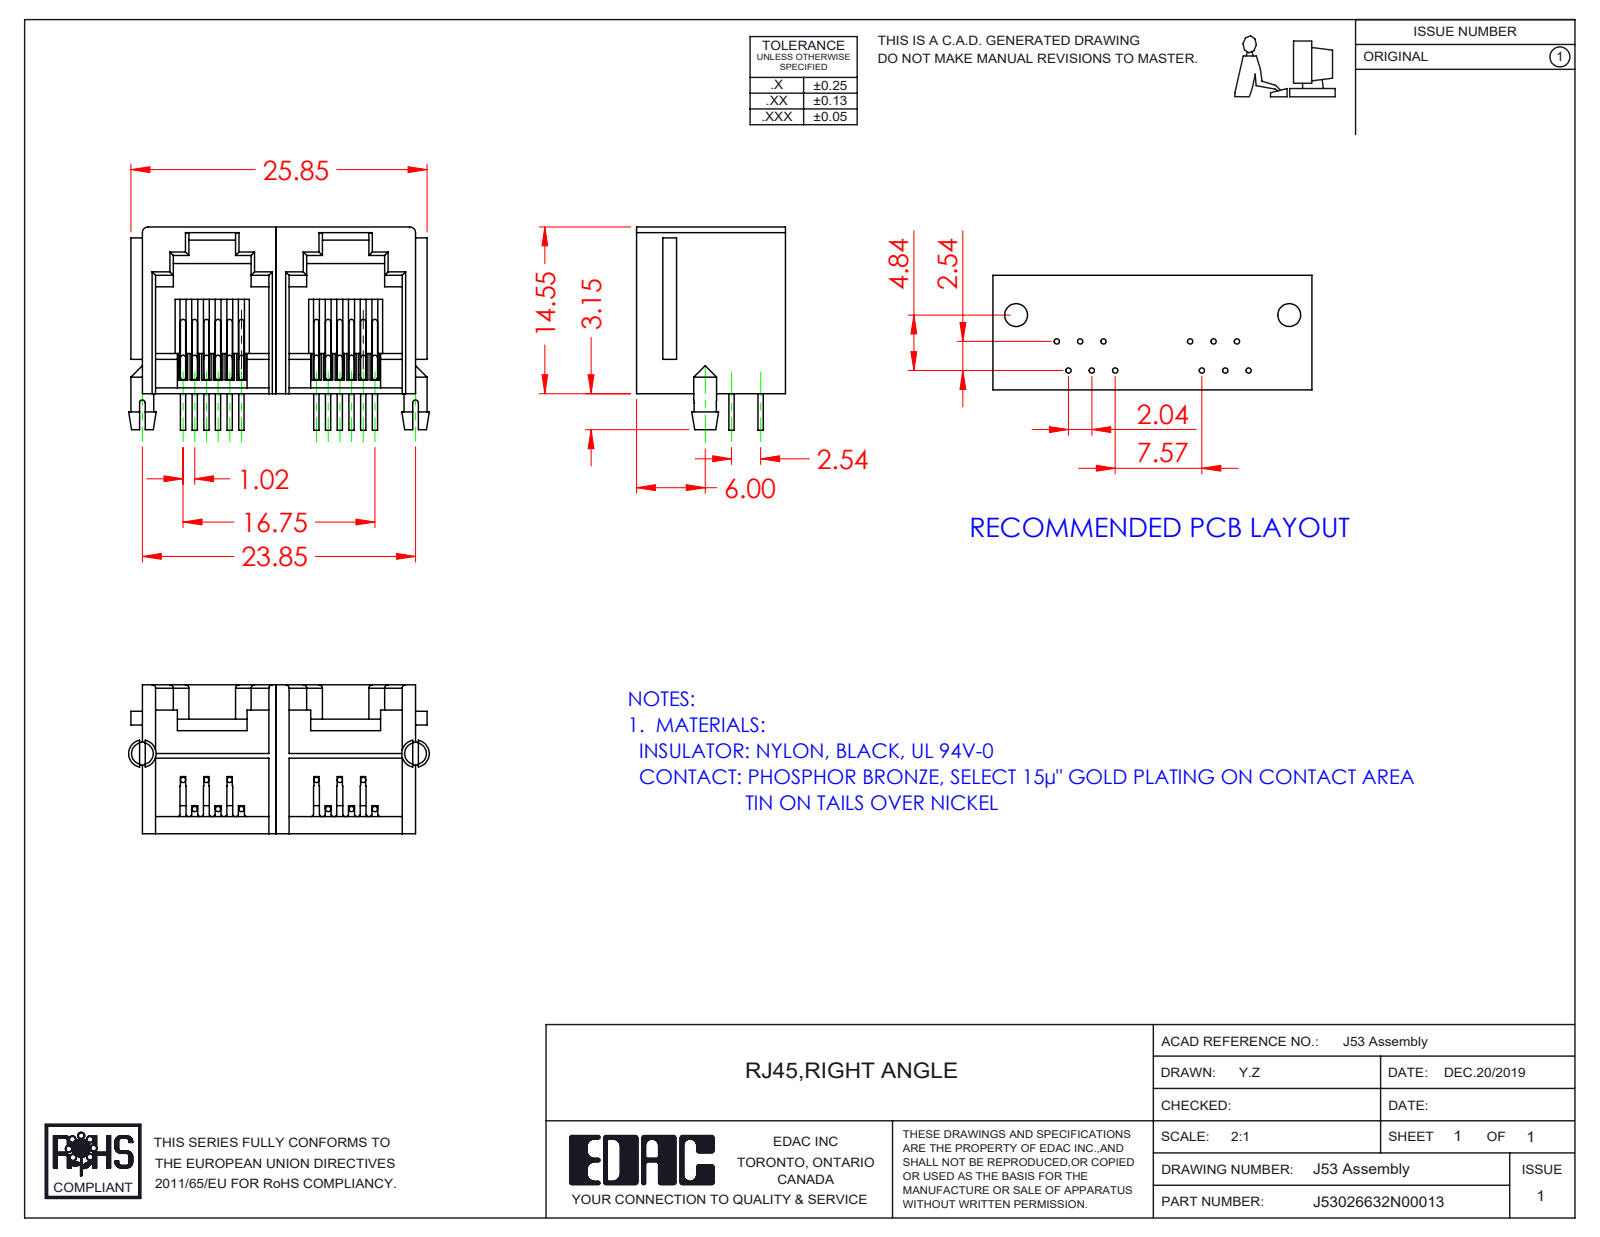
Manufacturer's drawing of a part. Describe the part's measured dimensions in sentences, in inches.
The part is named "53 Contact - 3; 53 Contact - 4; RJ53026632N00013; 53 Contact - 6 (+6 more)". Its 3-D file was written by "SolidWorks 2016 (CONFIG_CONTROL_DESIGN)". It is 14 solids with 595 faces: 410 planar, 128 cylindrical and 57 other. Overall it measures 1.033 by 0.699 by 0.512 inches. Its volume is 0.11 cubic inches and its surface area 6.634 square inches. Round bosses or shafts: 36 of diameter 0.018, 2 of diameter 0.079. Partial cylindrical surfaces (rounded edges, fillets, slot ends): 14 of radius 0.012, 10 of radius 0.02, 2 of radius 0.01, 1 of radius 0.026. The main face-to-face distances are 0.459, 0.046, 0.435, 0.48, 0.893, 0.413, 0.504, 0.024, 0.389, 0.118.
